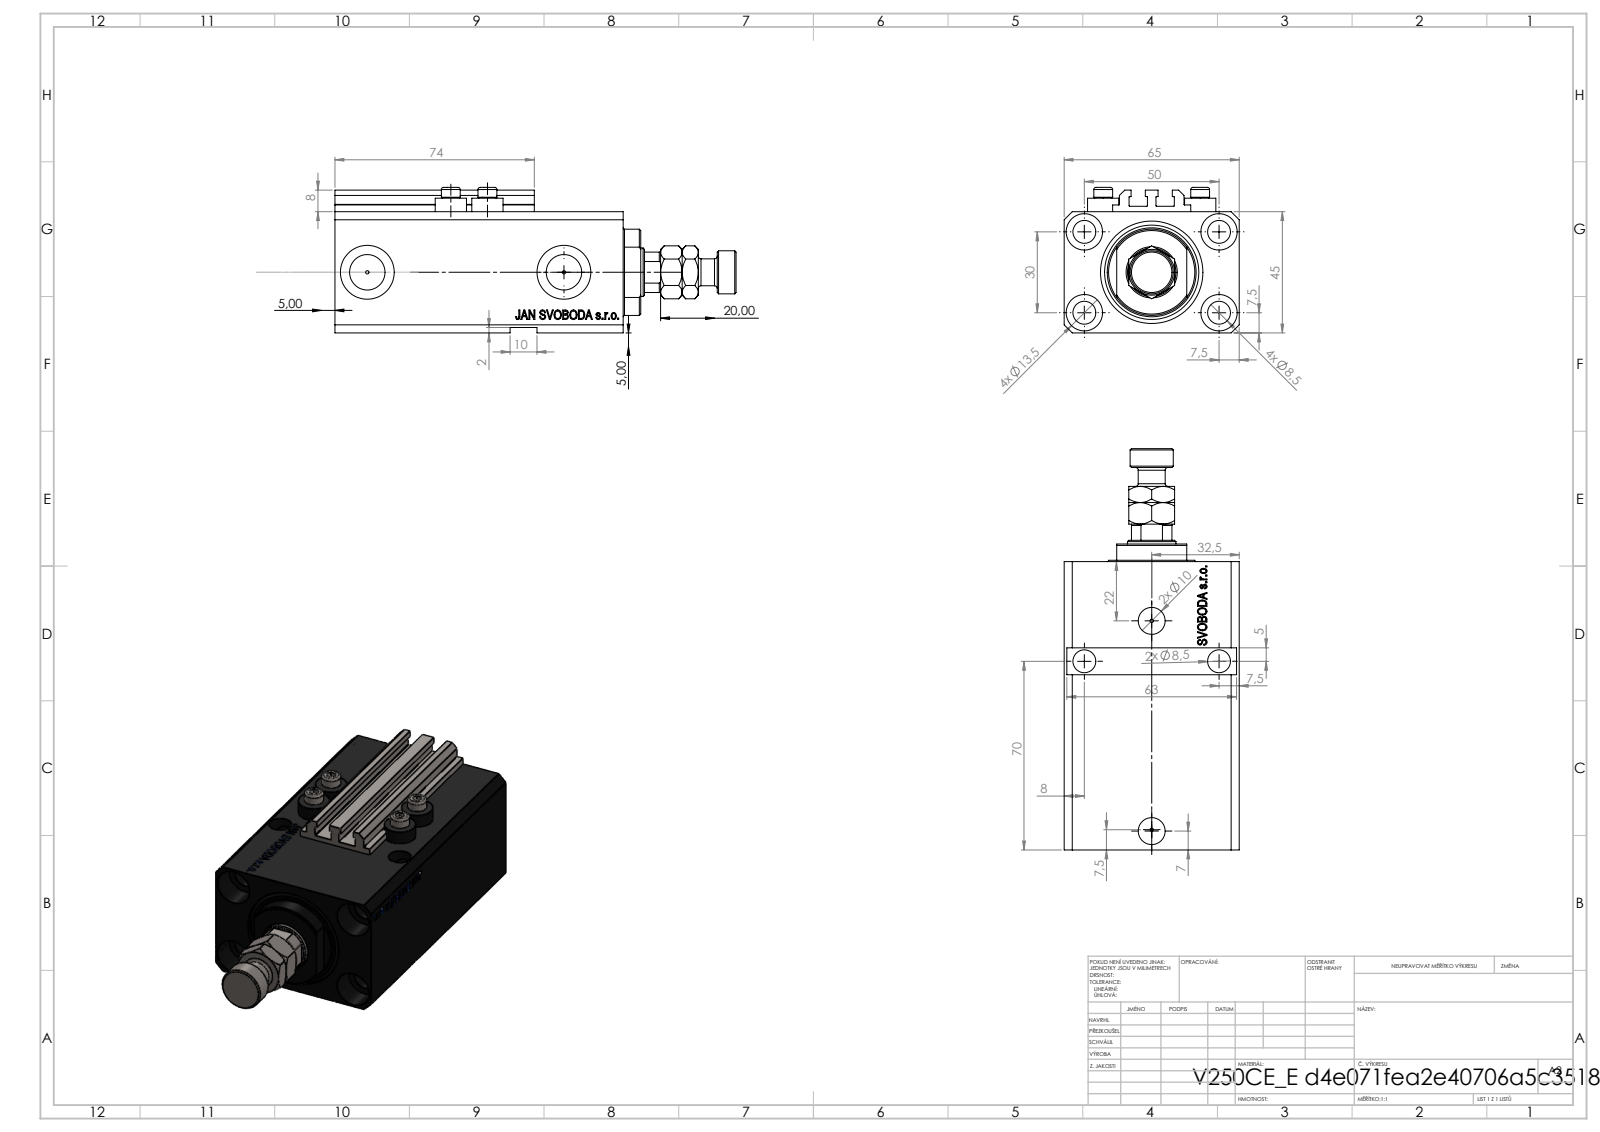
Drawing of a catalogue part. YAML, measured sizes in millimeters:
part_name: "ALLEN BOLT V250CE; V250CE_C_VCP; V250CE_VC_E; MFA (+1 more)"
step_written_by: "SolidWorks 2019 (CONFIG_CONTROL_DESIGN)"
units: millimeters
bodies: {solids: 9, faces: 1139, planar: 527, cylindrical: 150, other: 462}
overall_size: [149, 65, 54]
volume: 278825
surface_area: 78940
round_holes:
  - {diameter: 8.5, count: 9}
  - {diameter: 1.25, count: 4}
  - {diameter: 4, count: 4}
  - {diameter: 13.5, count: 4}
  - {diameter: 10, count: 2}
  - {diameter: 13.16, count: 2}
  - {diameter: 20, count: 2}
  - {diameter: 18, count: 1}
  - {diameter: 25, count: 1}
  - {diameter: 38, count: 1}
round_bosses_or_shafts:
  - {diameter: 11.6, count: 4}
  - {diameter: 7, count: 4}
  - {diameter: 16, count: 1}
  - {diameter: 10, count: 1}
partial_cylinders:
  - {radius: 0.2, count: 10}
  - {radius: 8.5, count: 1}
  - {radius: 16, count: 1}
face_to_face_distances: [45, 65, 14, 93, 2, 47, 107, 6.9, 20.5, 2.5]
hole_center_spacings: [29.15, 50, 13.6, 14.76, 15.12, 27.51, 27.89, 30]
